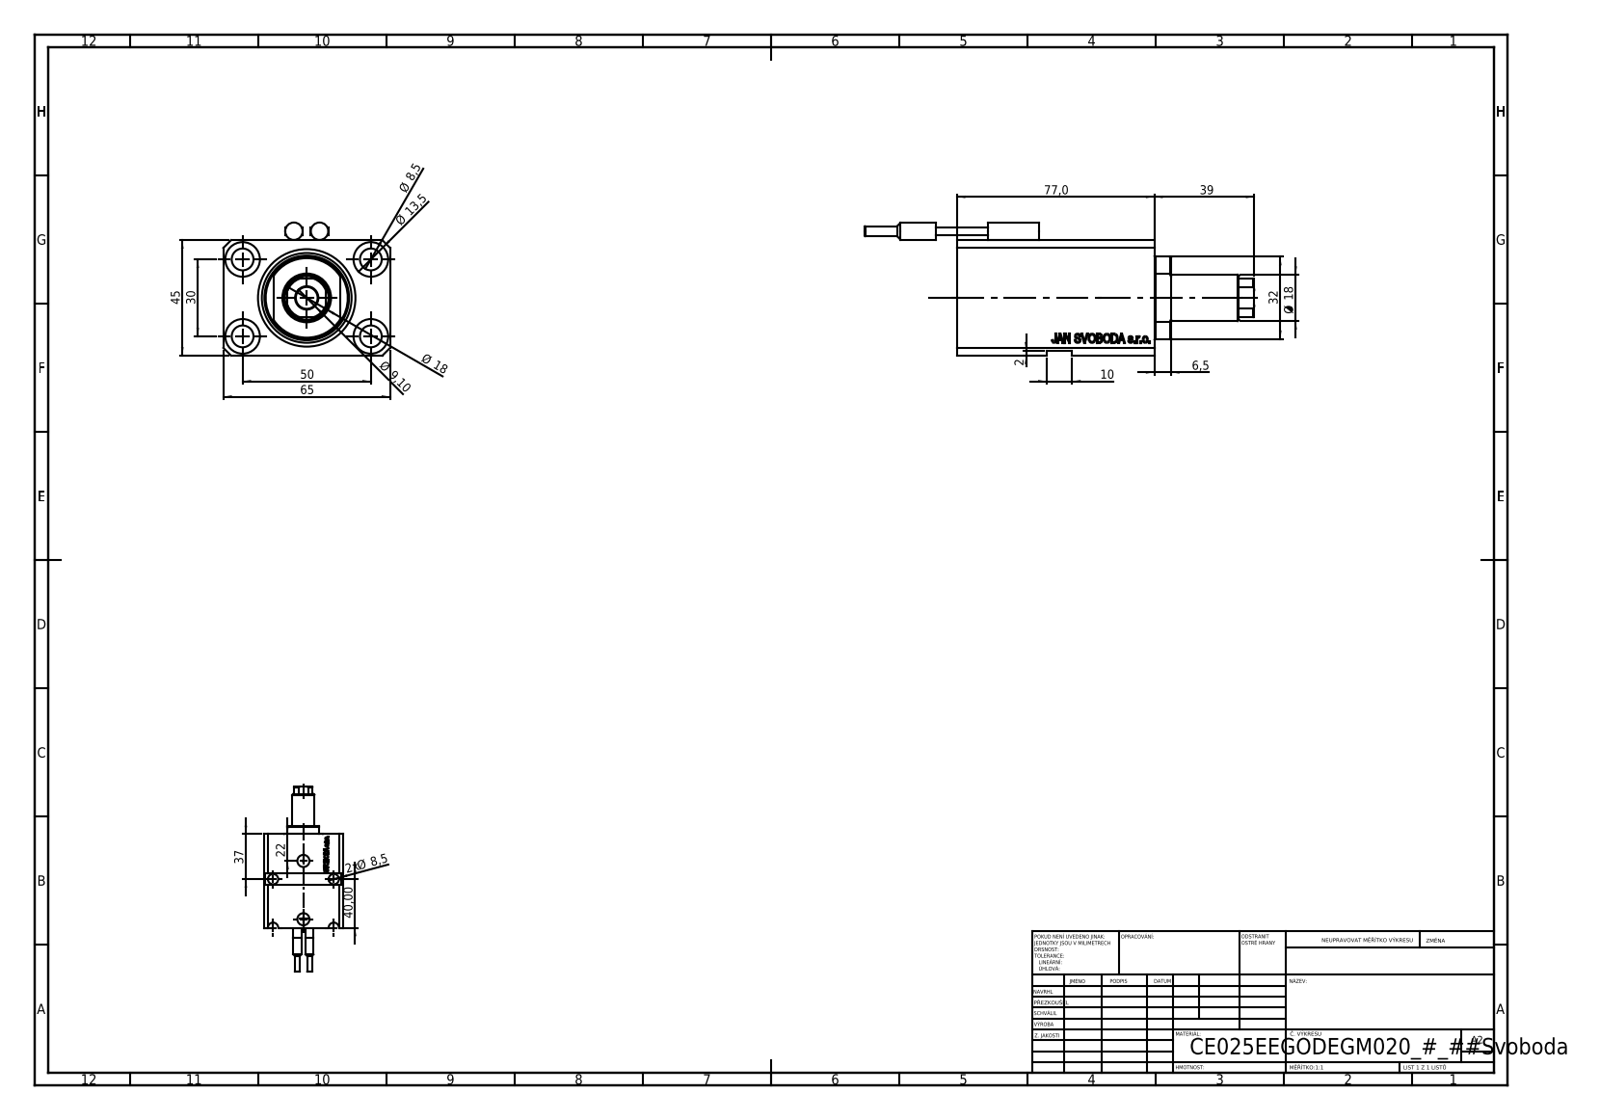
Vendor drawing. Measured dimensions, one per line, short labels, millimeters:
name: SWITCH_V250CE; V250CE_C_VCP; V250CE_E_Body; V250CE_VC_E
written by: SolidWorks 2019 (CONFIG_CONTROL_DESIGN)
unit: mm
bodies: 5 solids, 942 faces (466 planar, 90 cylindrical, 386 other)
size: 152 × 65 × 51.9
volume: 210 105 mm³; area: 53 901 mm²
holes: 7× ⌀8.5, 4× ⌀13.5, 2× ⌀1.25, 2× ⌀10, 1× ⌀18, 1× ⌀25, 1× ⌀38
bosses: 2× ⌀6.8, 2× ⌀6.5, 2× ⌀4
rounds: 2× R4.25, 1× R8.5, 1× R16
face distances: 45, 65, 51.9, 77, 25.1, 32, 19.9, 2, 68, 9
hole spacings: 29.15, 50, 30, 40.98, 41.4, 58.31, 0.53, 47.47
